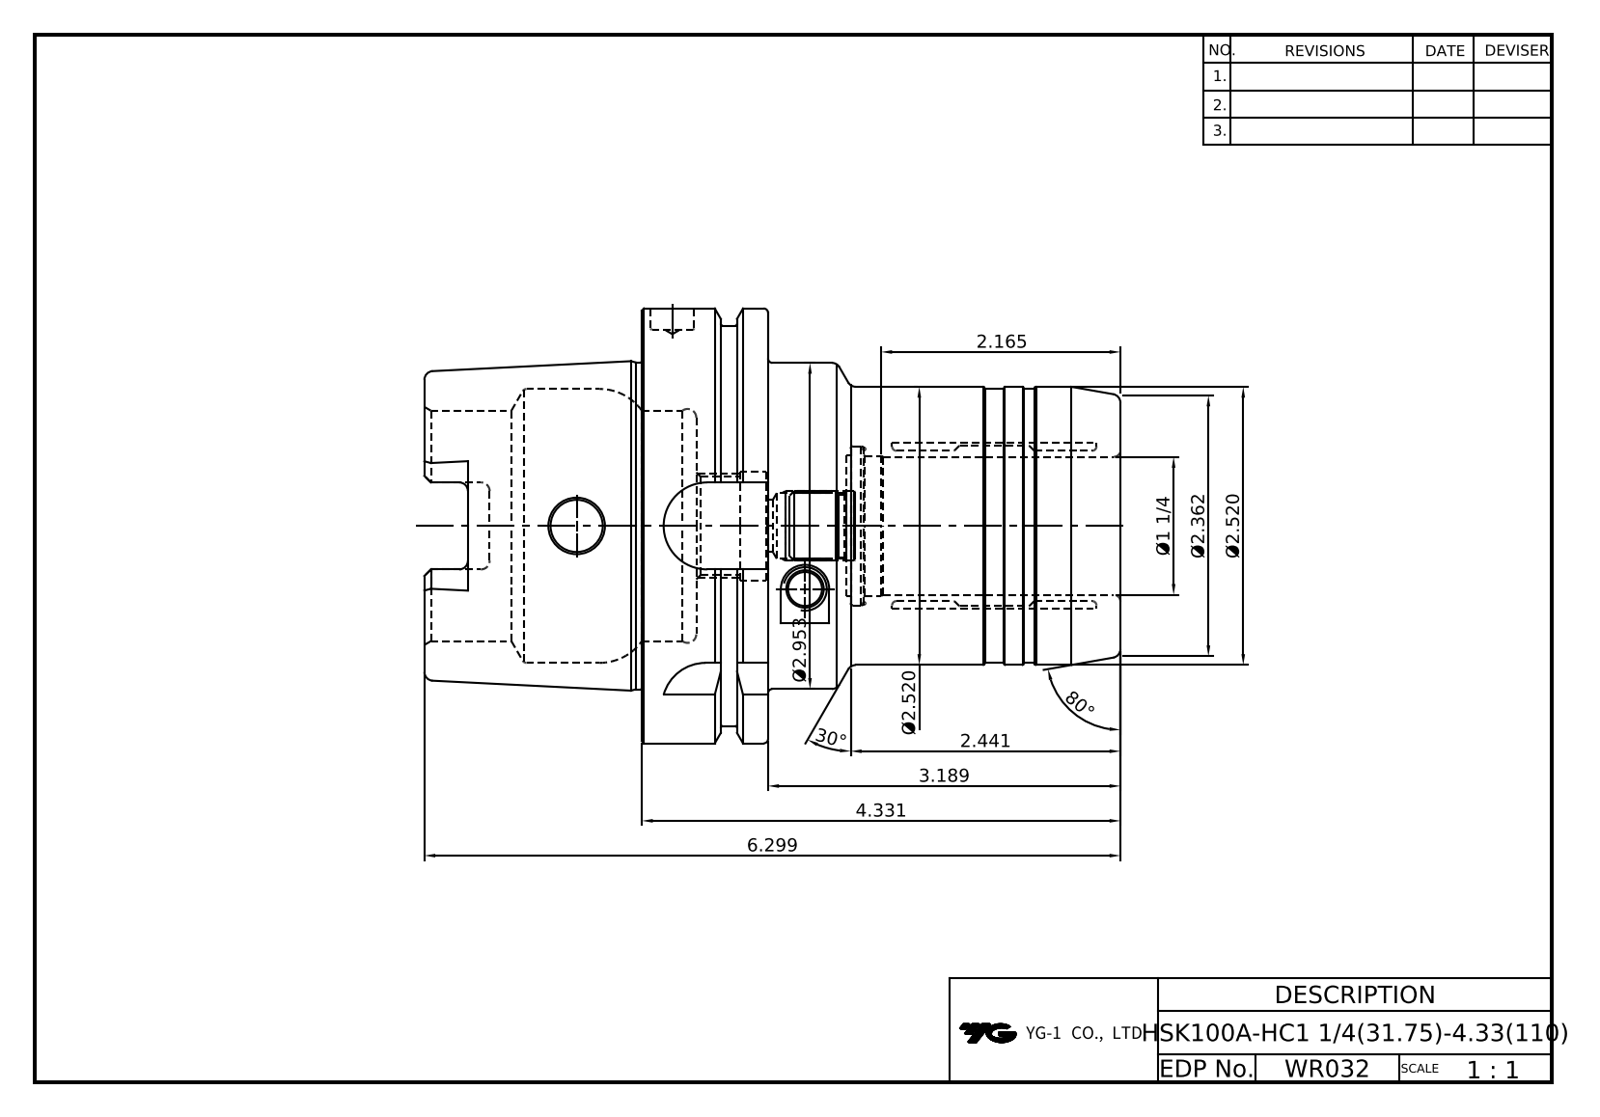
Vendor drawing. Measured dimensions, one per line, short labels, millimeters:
name: HSK100A-HC31.75-110
written by: Autodesk Inventor 2020 (AUTOMOTIVE_DESIGN)
unit: mm
bodies: 1 solid, 136 faces (38 planar, 40 cylindrical, 58 other)
size: 160 × 100 × 100
volume: 479 823 mm³; area: 72 483 mm²
holes: 2× ⌀12, 1× ⌀10, 1× ⌀14.92, 1× ⌀22.38, 1× ⌀25, 1× ⌀31.75, 1× ⌀32.6, 1× ⌀53
bosses: 1× ⌀100, 1× ⌀92, 1× ⌀75.41, 1× ⌀75, 1× ⌀64, 1× ⌀63
rounds: 6× R2, 4× R4.88, 4× R10
face distances: 29, 110, 81, 12.5, 16.5, 97.5, 62.5, 50, 79, 160
